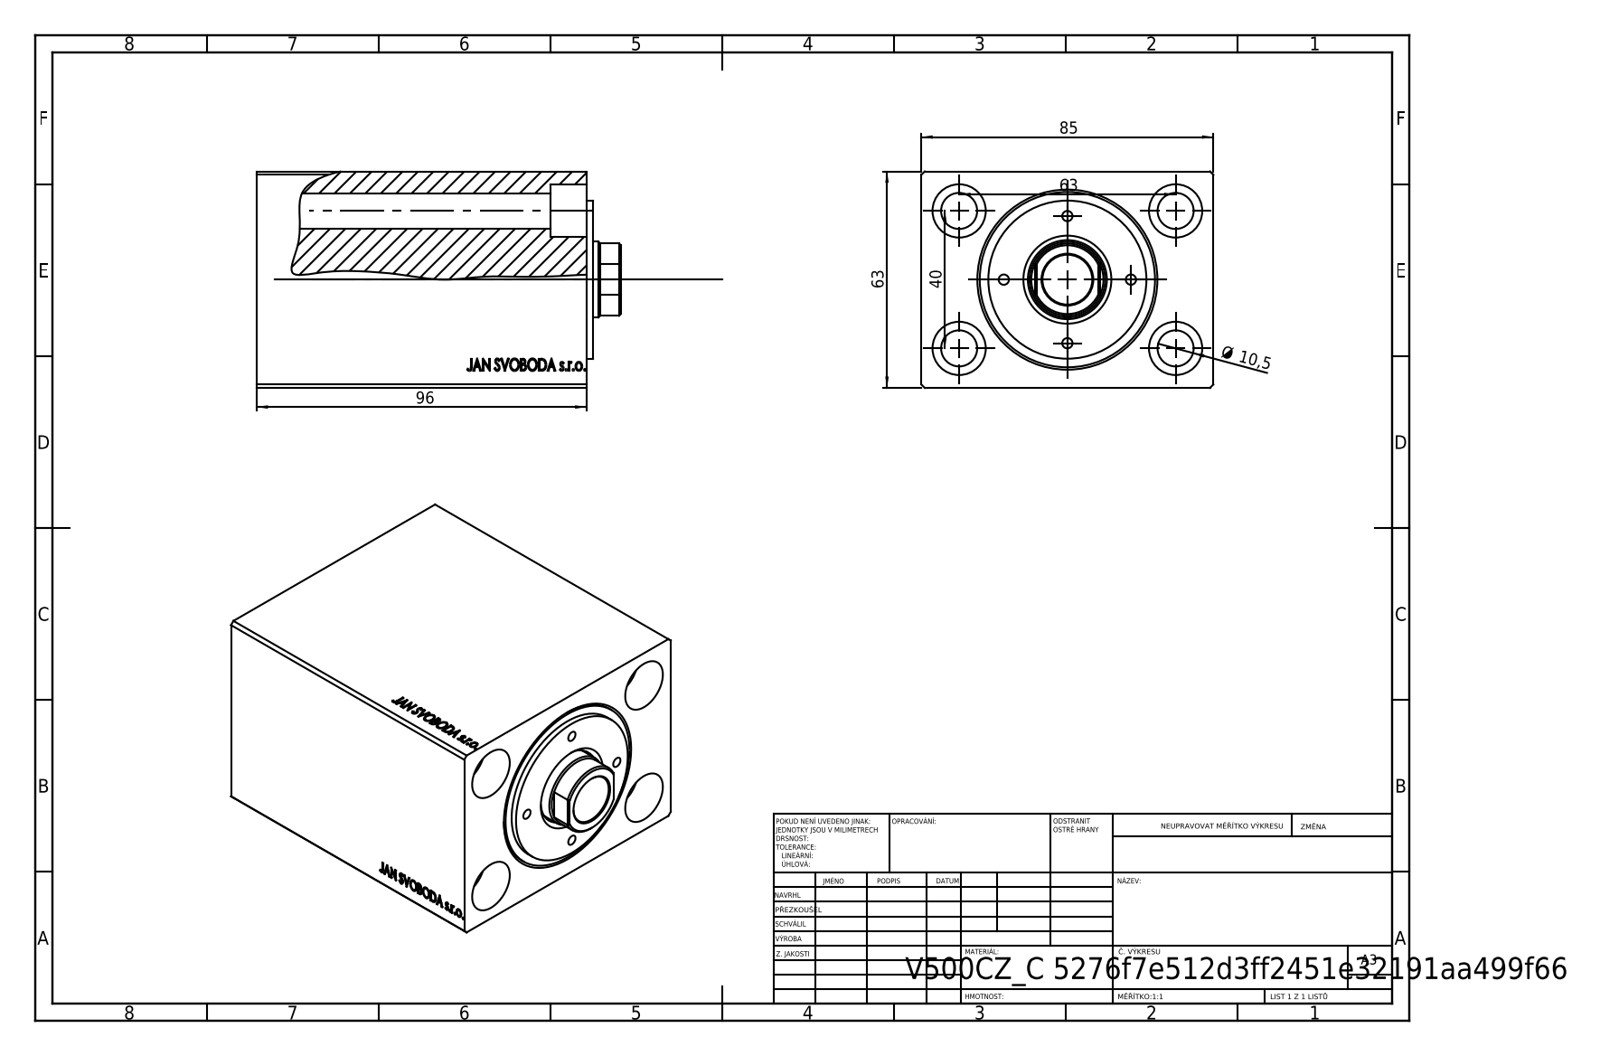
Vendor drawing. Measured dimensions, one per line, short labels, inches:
written by: SolidWorks 2019 (CONFIG_CONTROL_DESIGN)
unit: in
bodies: 1 solid, 818 faces (394 planar, 42 cylindrical, 382 other)
size: 3.78 × 3.346 × 2.48
volume: 18.9 in³; area: 102.7 in²
holes: 4× ⌀0.413, 4× ⌀0.61, 2× ⌀0.217, 2× ⌀0.535, 2× ⌀0.787, 1× ⌀1.417, 1× ⌀1.575, 1× ⌀2.008
face distances: 2.48, 3.346, 3.78, 3.201, 0.579, 3.772, 0.571, 0.407, 3.373, 2.795
hole spacings: 1.469, 1.575, 2.48, 2.938, 2.283
